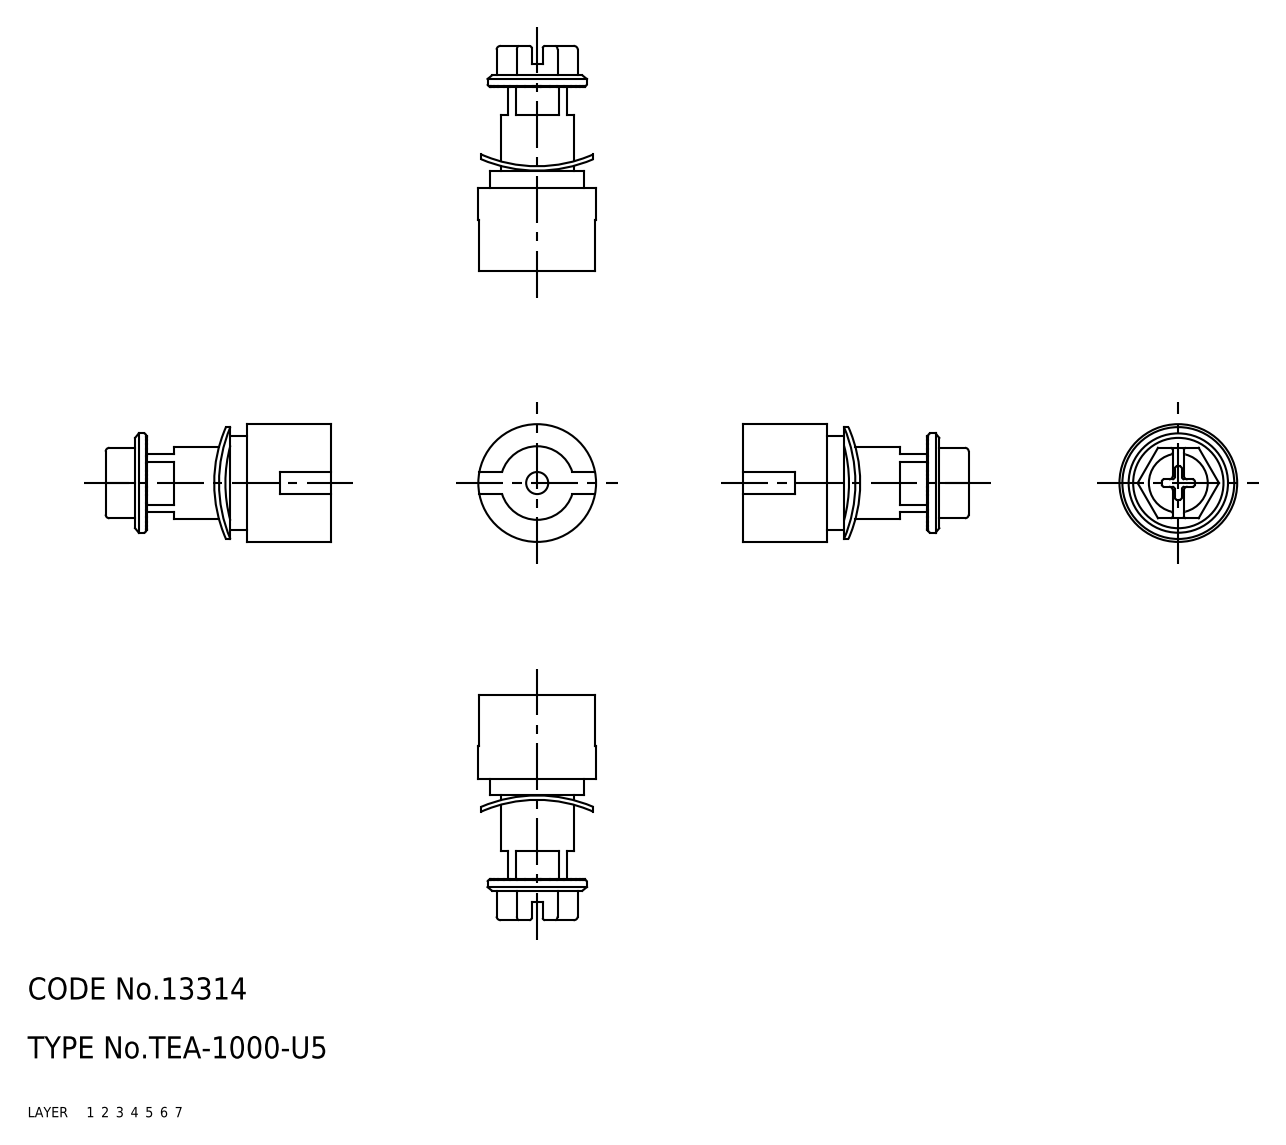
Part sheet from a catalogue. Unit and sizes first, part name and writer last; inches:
Units: inches
Overall size (bounding box): 1.219 × 0.63 × 0.63
Volume: 0.203 in³ · Surface area: 3.732 in²
Bodies: 1 solid, 144 faces (0 planar, 0 cylindrical, 144 other)
Part name (STEP PRODUCT): shaft
STEP written by: CADfix (AUTOMOTIVE_DESIGN)
